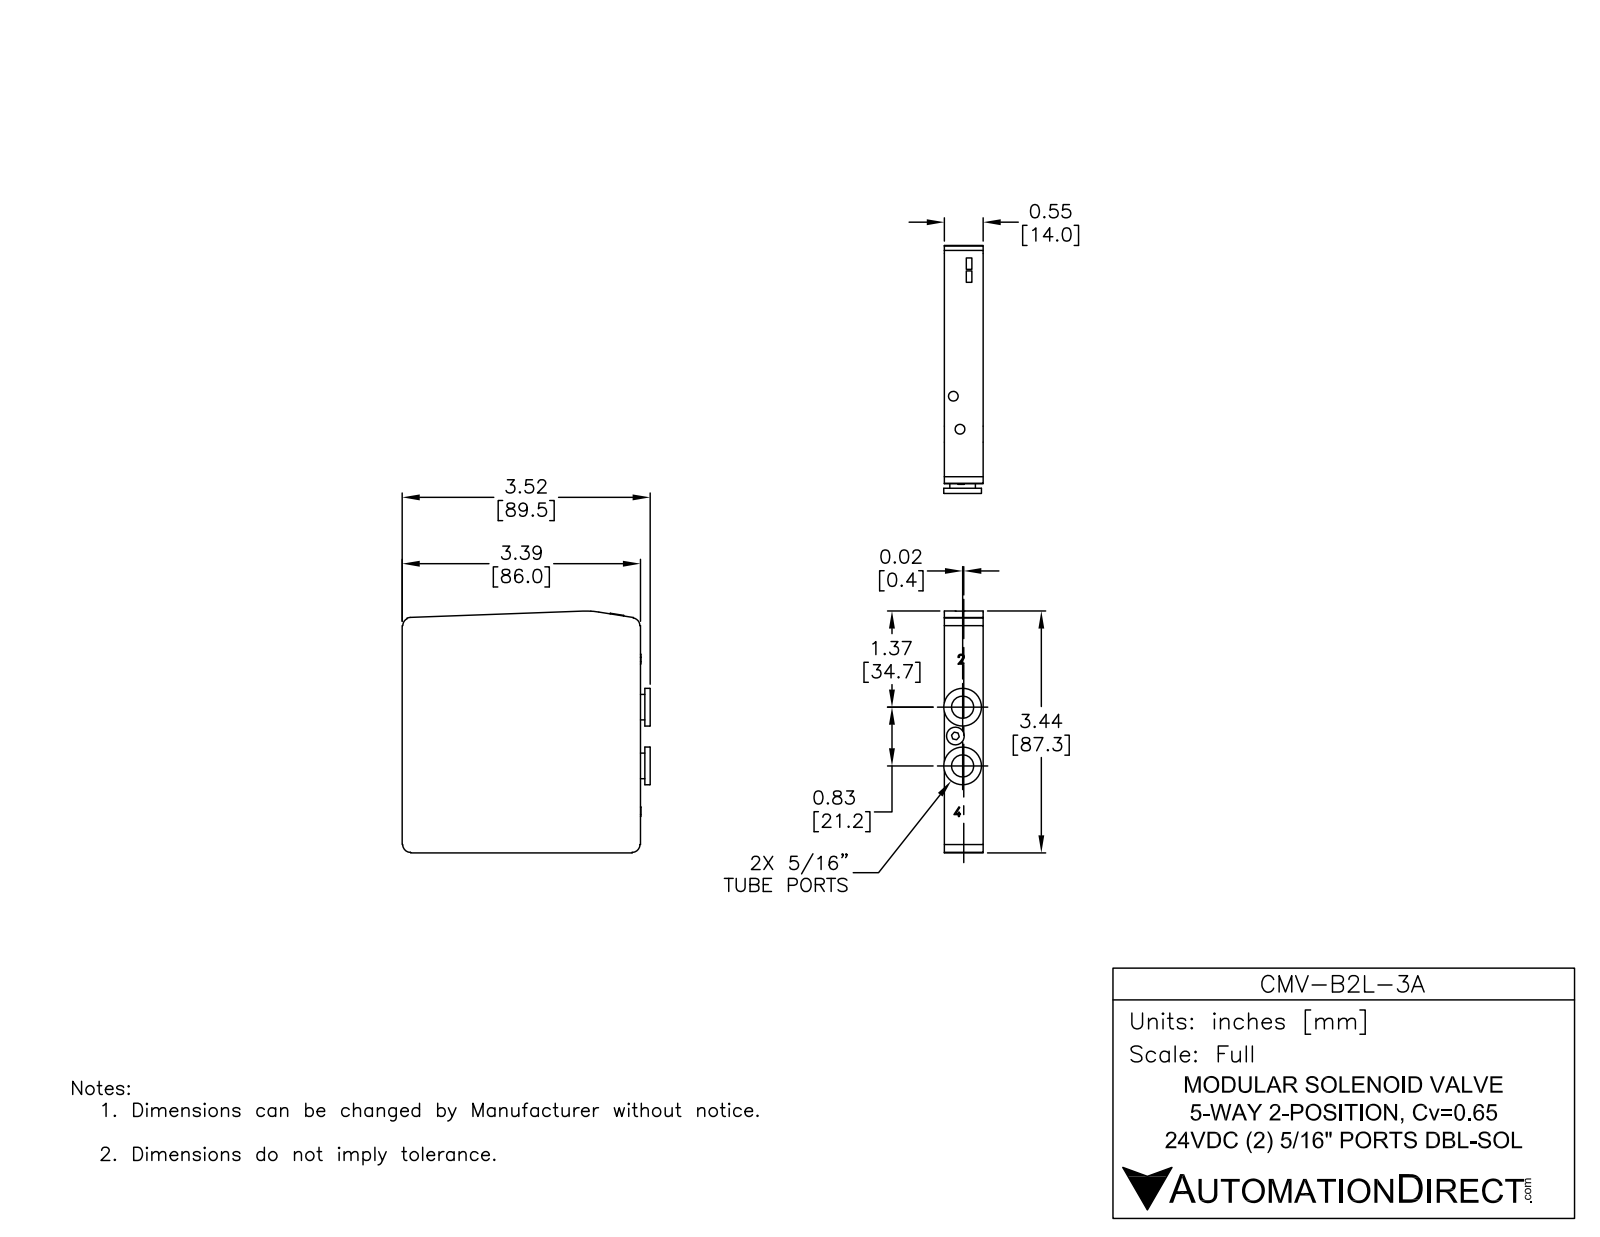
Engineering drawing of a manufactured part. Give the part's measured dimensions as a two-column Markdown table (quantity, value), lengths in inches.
| quantity | value |
| --- | --- |
| part name | CMV-B2L-3A |
| STEP written by | SolidWorks 2013 (AUTOMOTIVE_DESIGN) |
| units | inches |
| bodies | 78 solids, 1154 faces (876 planar, 162 cylindrical, 116 other) |
| overall size | 3.524 × 3.437 × 0.903 |
| volume | 5.824 in³ |
| surface area | 73.23 in² |
| round holes (diameter × count) | 0.207 × 4, 0.132 × 2, 0.173 × 2, 0.256 × 2, 0.315 × 2, 0.386 × 2, 0.453 × 2, 0.142 × 1, 0.177 × 1, 0.246 × 1, 0.252 × 1 |
| round bosses / shafts (diameter × count) | 0.059 × 4, 0.535 × 2, 0.362 × 2, 0.246 × 2, 0.226 × 2, 0.165 × 2, 0.157 × 2, 0.138 × 1 |
| partial cylindrical surfaces (radius × count) | 0.093 × 12, 0.031 × 4, 0.059 × 4, 0.11 × 4, 0.039 × 2, 0.006 × 1, 0.007 × 1, 0.01 × 1 |
| main face-to-face distances | 0.551, 0.157, 0.394, 0.118, 0.039, 3.268, 0.197, 0.591, 1.171, 0.564 |
| hole center spacings | 0.382, 0.787, 0.873, 0.341, 0.341, 0.342, 0.372, 0.418 |
